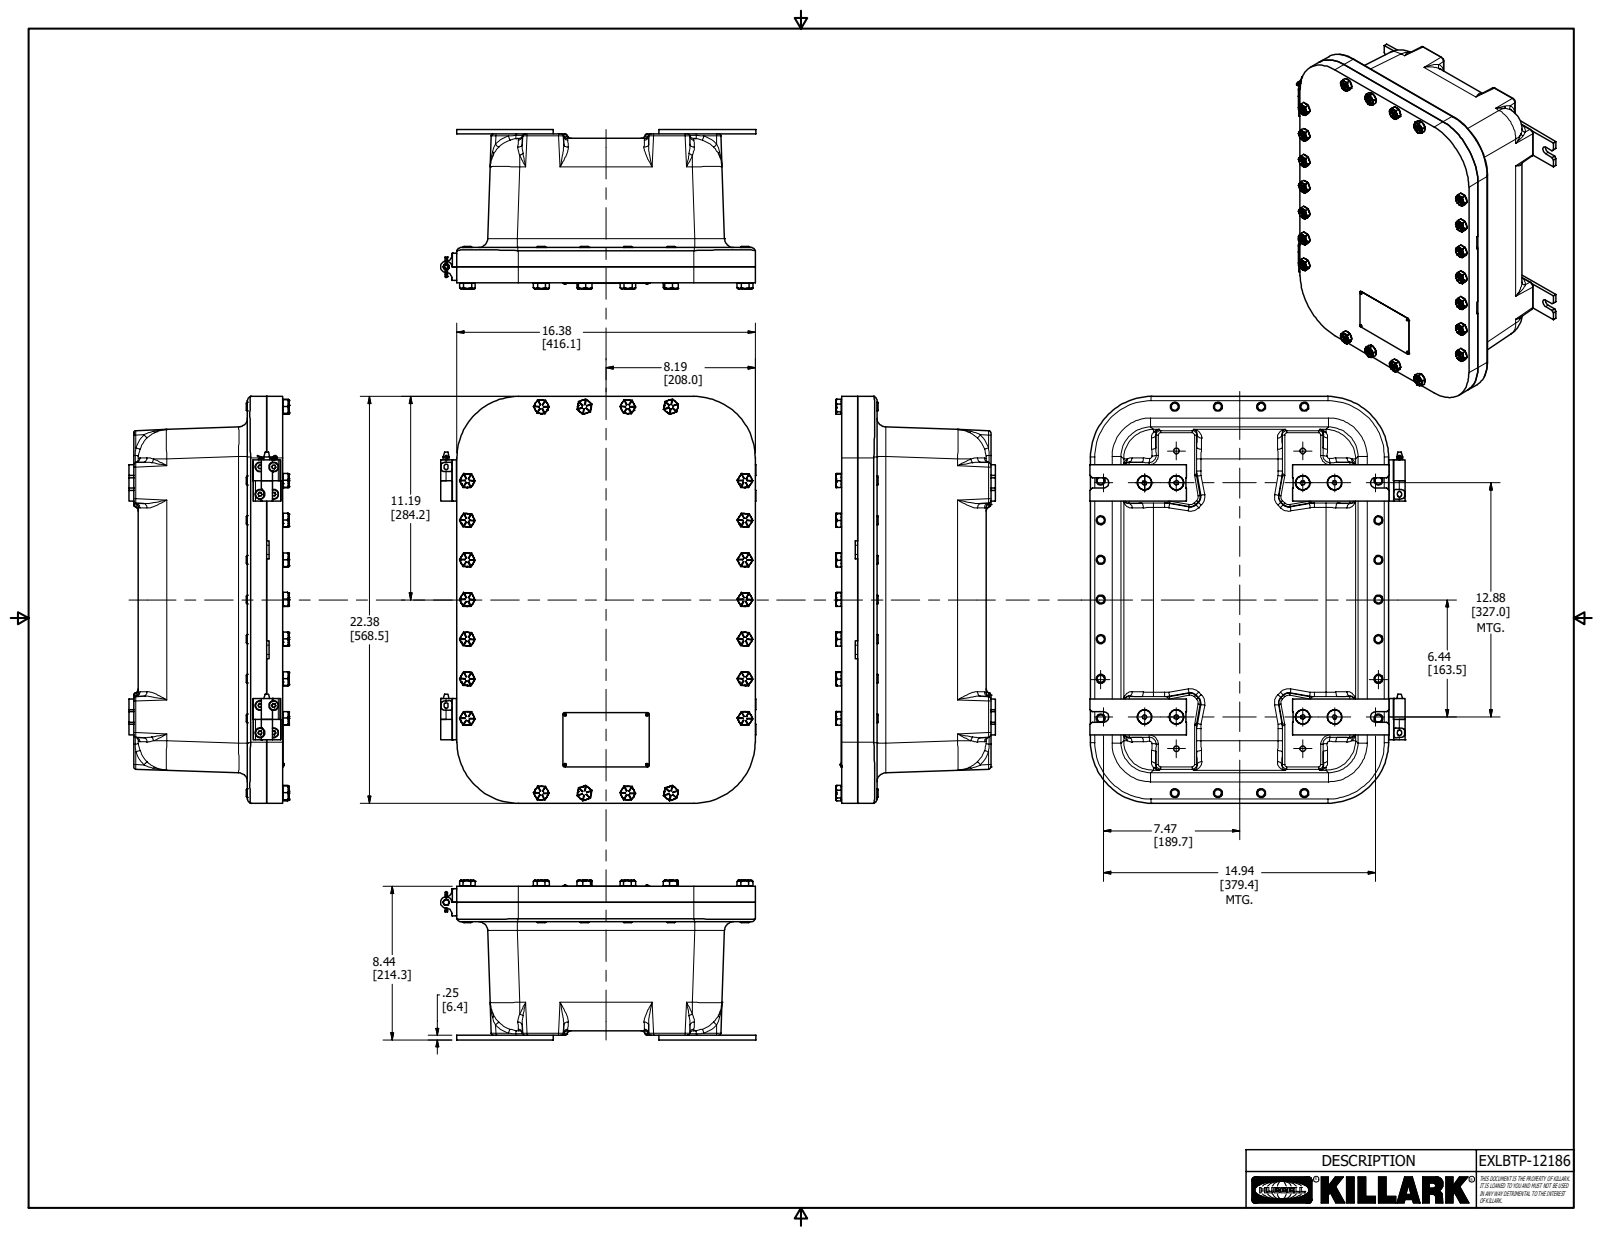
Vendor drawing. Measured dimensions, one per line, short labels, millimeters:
name: EXBLTP - 12186 N4; 51305ABAM (EXBLT-12186); 25328AAAM; 0720361B (+8 more)
written by: Autodesk Inventor 2020 (AUTOMOTIVE_DESIGN)
unit: mm
bodies: 57 solids, 3442 faces (2284 planar, 413 cylindrical, 745 other)
size: 568.5 × 439.8 × 222.8
volume: 13 670 000 mm³; area: 1 723 000 mm²
holes: 26× ⌀13.5, 22× ⌀10.6, 16× ⌀7.8, 8× ⌀5.6, 8× ⌀6.8, 8× ⌀10.3, 5× ⌀2.8, 4× ⌀0.6, 1× ⌀8.1
bosses: 22× ⌀19.1, 22× ⌀12.4, 8× ⌀12.4, 8× ⌀9.3, 8× ⌀6.2, 4× ⌀2.5, 4× ⌀2.1, 1× ⌀15.7
rounds: 48× R2.3, 44× R6.4, 29× R3.2, 16× R0.8, 12× R1.1, 8× R25.4, 8× R41.3, 4× R7.1
face distances: 22.2, 15.9, 163.5, 185.8, 6.4, 179.4, 201.6, 15.8, 185.7, 22.2
hole spacings: 391.3, 333.2, 387.4, 336.2, 403, 19.1, 38.1, 42.6
